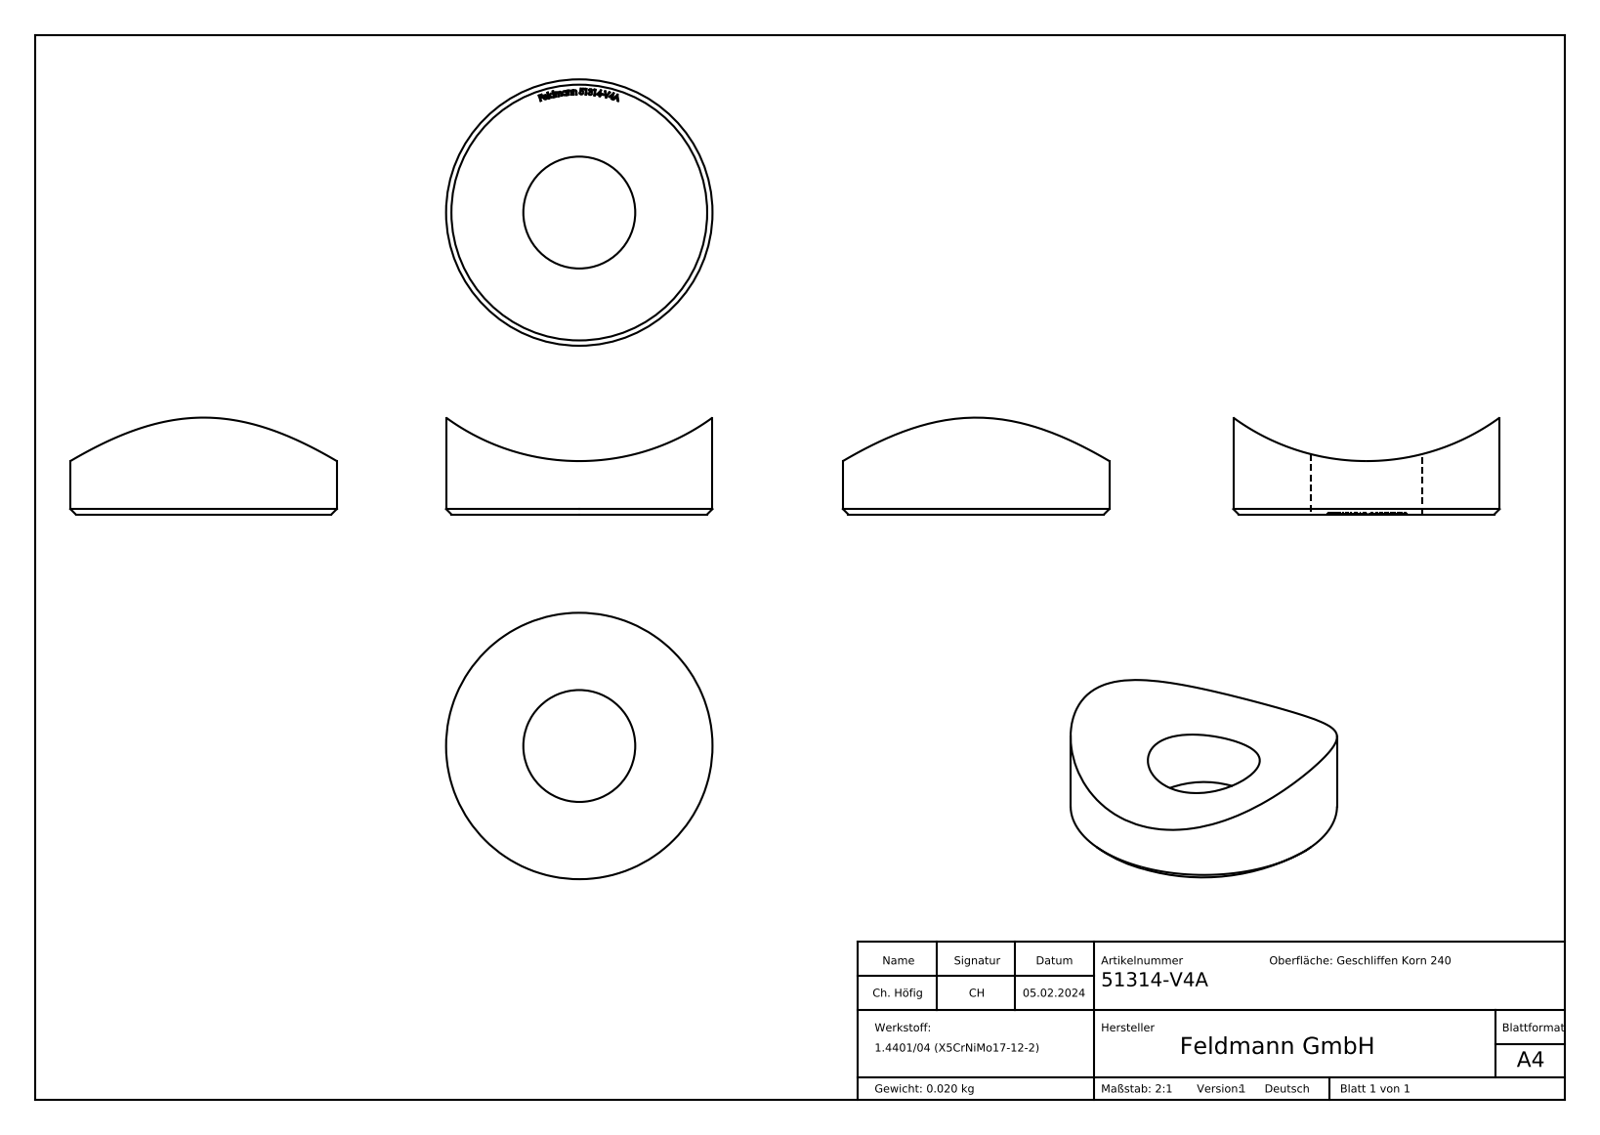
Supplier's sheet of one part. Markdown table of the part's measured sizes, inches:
| quantity | value |
| --- | --- |
| part name | 51314-V4A |
| STEP written by | SolidWorks 2018 (CONFIG_CONTROL_DESIGN) |
| units | inches |
| bodies | 1 solid, 221 faces (147 planar, 3 cylindrical, 71 other) |
| overall size | 0.984 × 0.984 × 0.357 |
| volume | 0.151 in³ |
| surface area | 2.382 in² |
| round holes (diameter × count) | 0.413 × 1 |
| round bosses / shafts (diameter × count) | 0.984 × 1 |
| partial cylindrical surfaces (radius × count) | 0.835 × 1 |
| main face-to-face distances | 0.185, 0.185, 0.16, 0.162, 0.015, 0.013, 0.172, 0.183, 0.012, 0.173 |
